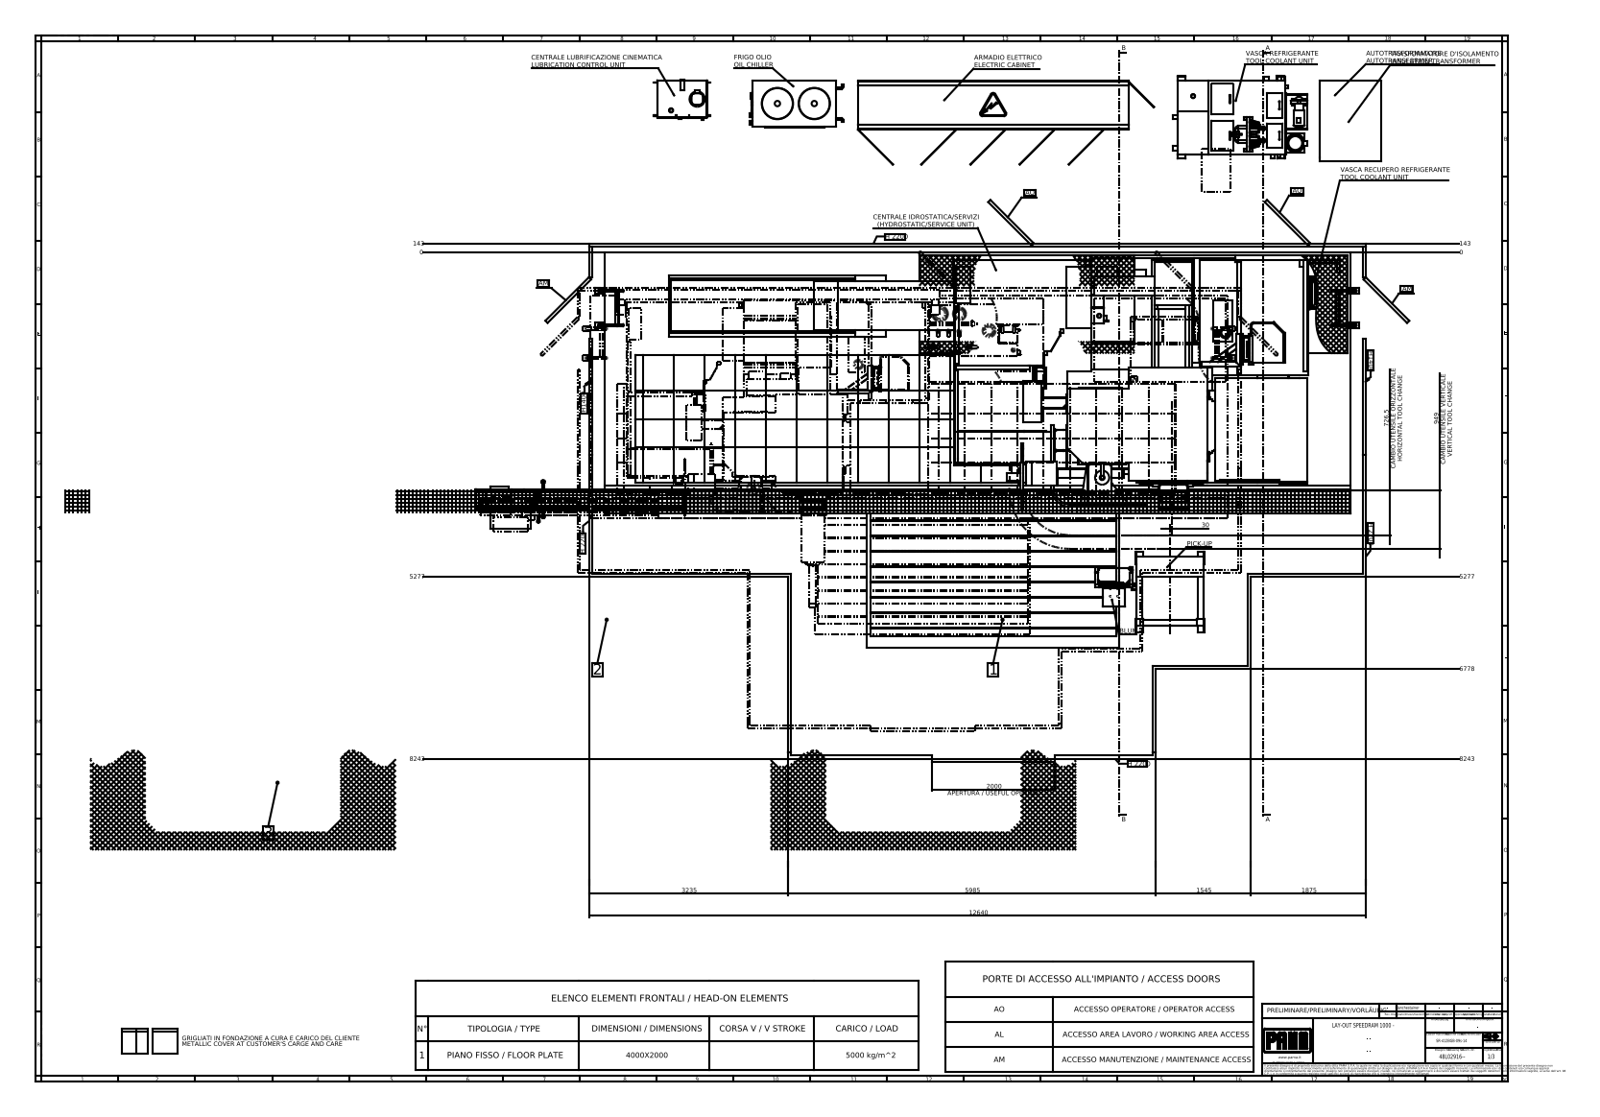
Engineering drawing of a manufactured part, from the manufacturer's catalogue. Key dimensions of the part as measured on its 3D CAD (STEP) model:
Part name (STEP PRODUCT): S003229_NO CARTERATURA; S003265_Y=2000; S001560_2 (1+1) POSTI; S001570_RETE - 1000 L (+8 more)
STEP written by: SolidWorks 2023 (AUTOMOTIVE_DESIGN)
Units: millimetres
Bodies: 401 solids, 6304 faces (4429 planar, 1421 cylindrical, 454 other)
Overall size (bounding box): 16140 × 14057.4 × 7912.5
Volume: 412 000 000 000 mm³ · Surface area: 1 601 000 000 mm²
Round holes (diameter × count): ⌀35 ×64, ⌀69.6 ×63, ⌀37.2 ×18, ⌀30 ×9, ⌀13 ×8, ⌀14 ×8, ⌀8 ×6, ⌀12.5 ×4, ⌀56.66 ×4, ⌀60 ×4, ⌀25.6 ×3, ⌀50 ×3
Round bosses / shafts (diameter × count): ⌀42.4 ×18, ⌀20 ×14, ⌀40 ×11, ⌀9 ×10, ⌀55 ×8, ⌀66.3 ×7, ⌀60 ×6, ⌀35 ×6
Partial cylindrical surfaces — rounded edges, fillets, slot ends (radius × count): R5 ×128, R15 ×53, R8 ×52, R35 ×26, R6 ×25, R3 ×21, R4 ×21, R10 ×20
Main face-to-face distances: 2000, 50, 1247, 753, 5, 10, 13986, 16140, 2650, 2700
Hole centre spacings: 273.13, 500, 1235.56, 758.02, 1423.59, 1000, 130, 260
